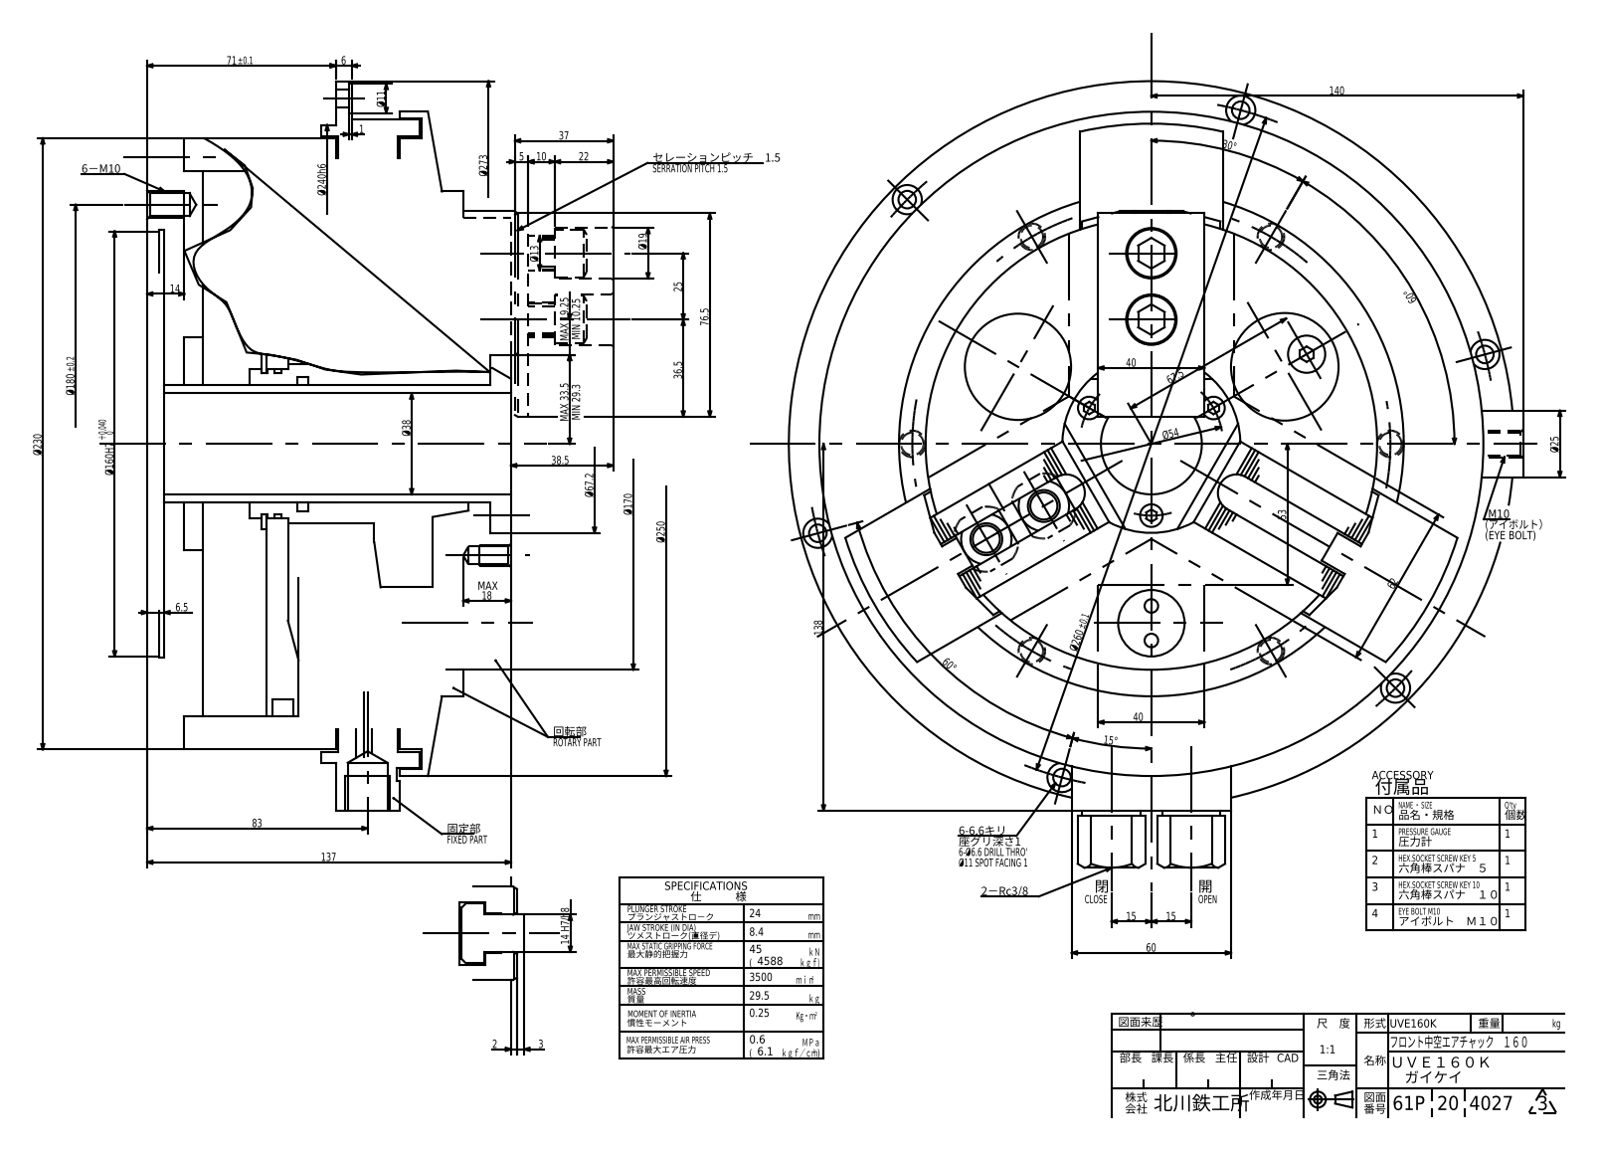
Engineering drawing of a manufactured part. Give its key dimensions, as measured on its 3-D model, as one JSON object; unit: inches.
{"part_name": "UVE160K", "step_written_by": "ST-DEVELOPER v16.7 (AUTOMOTIVE_DESIGN)", "units": "inches", "bodies": {"solids": 1, "faces": 1278, "planar": 815, "cylindrical": 297, "other": 166}, "overall_size": [11.654, 10.886, 6.909], "volume_in3": 338.5, "surface_area_in2": 570.4, "round_holes": [[0.26, 20], [0.433, 15], [0.236, 14], [0.197, 10], [0.472, 9], [0.394, 7], [0.512, 6], [0.075, 3], [0.217, 3], [0.374, 3], [0.201, 2], [0.406, 2]], "round_bosses_or_shafts": [[0.394, 9], [0.748, 6], [0.709, 6], [0.236, 4], [0.335, 3], [0.197, 3], [0.984, 2], [0.866, 2]], "partial_cylinders_radius": [[0.024, 12], [0.079, 6], [0.482, 6], [0.236, 5], [0.295, 3], [0.463, 3], [0.591, 2], [1.22, 1]], "face_to_face_distances": [0.256, 0.236, 2.539, 2.795, 5.394, 0.02, 1.575, 5.138, 2.598, 0.748], "hole_center_spacings": [3.543, 4.252, 5.118, 5.466, 7.365, 8.375, 1.928, 2.676]}
